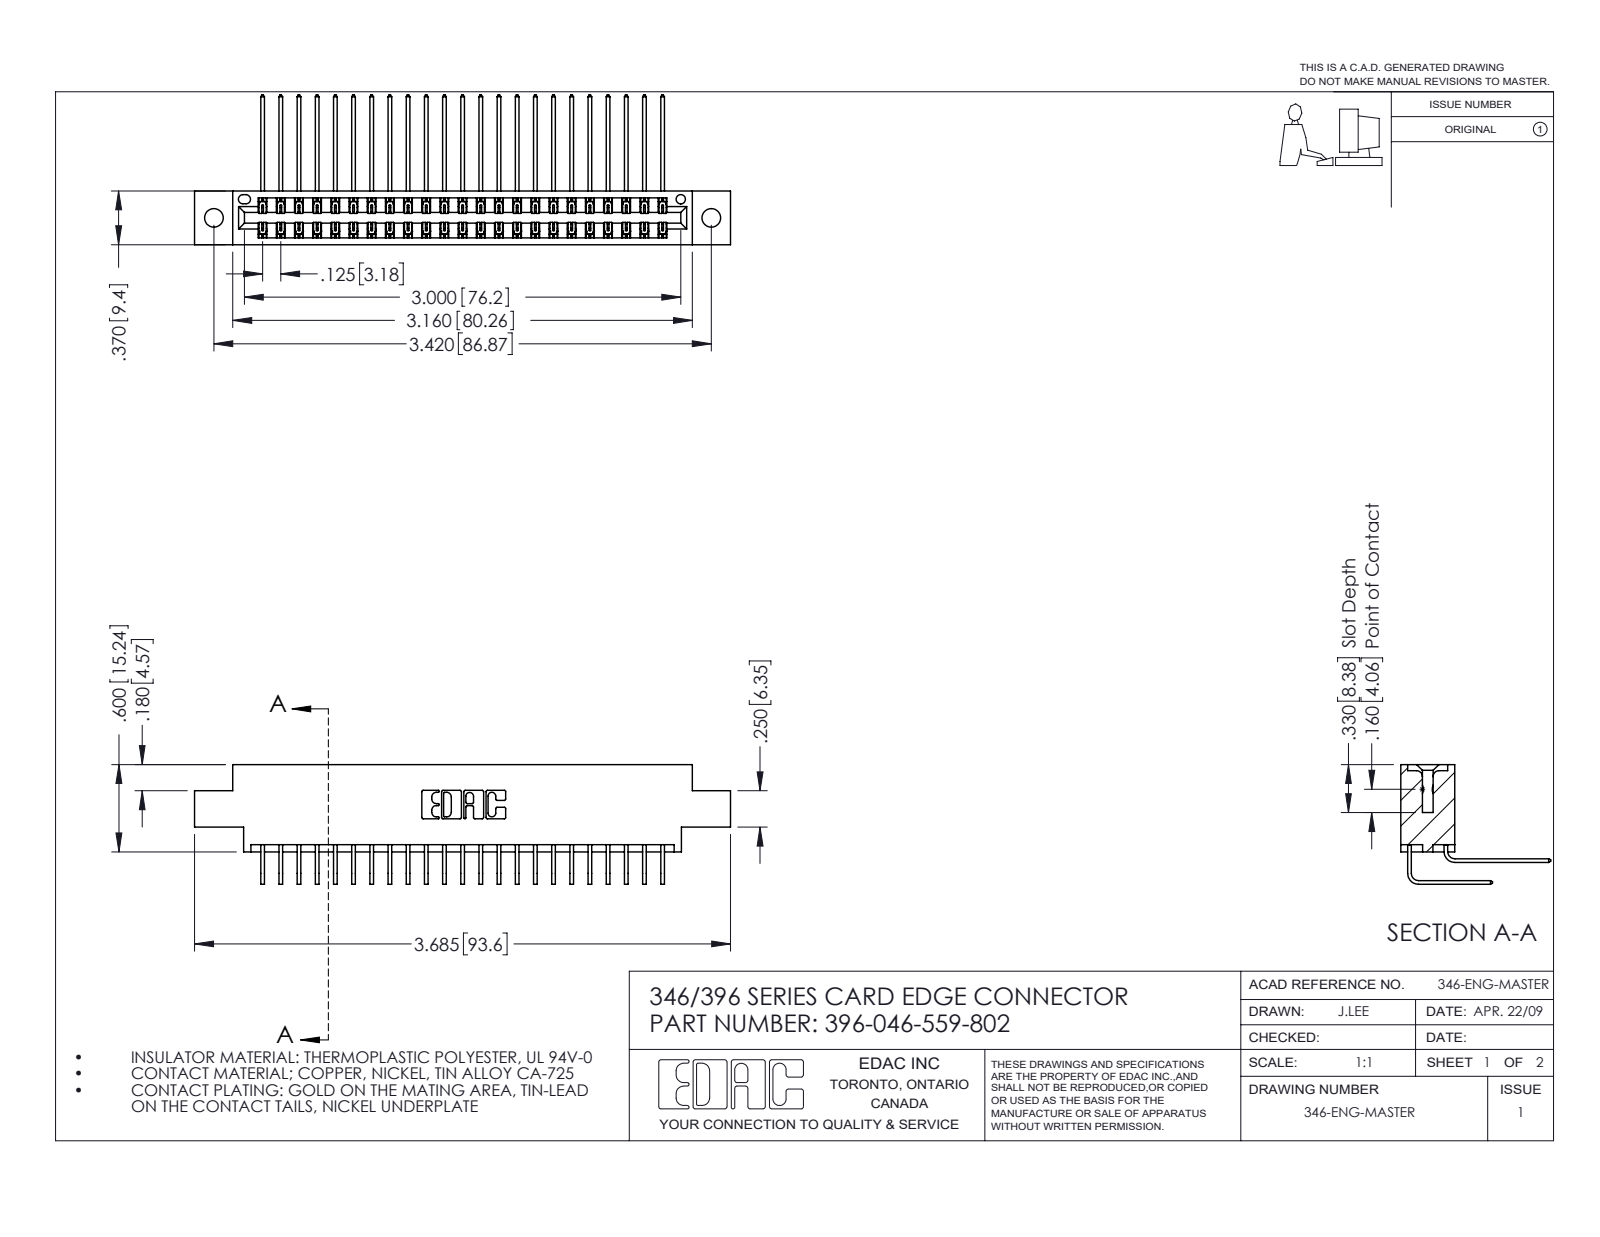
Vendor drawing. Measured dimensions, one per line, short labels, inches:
name: 345-292-001_558 559 Tail - 1; 345-292-001_559 Tail - 2; 396-046-559-802; 346 Part_0.170 Offset - 0.128 Dia
written by: SolidWorks 2016 (CONFIG_CONTROL_DESIGN)
unit: in
bodies: 47 solids, 2610 faces (1782 planar, 828 cylindrical, 0 other)
size: 3.685 × 1.03 × 0.823
volume: 0.552 in³; area: 20.66 in²
holes: 2× ⌀0.128, 1× ⌀0.064
rounds: 69× R0.006, 22× R0.01, 6× R0.007, 6× R0.031, 3× R0.026, 2× R0.014, 2× R0.022, 2× R0.024
face distances: 0.048, 0.322, 0.37, 0.025, 0.25, 0.072, 0.298, 0.275, 0.15, 0.148
hole spacings: 0.246, 3.212, 3.42
